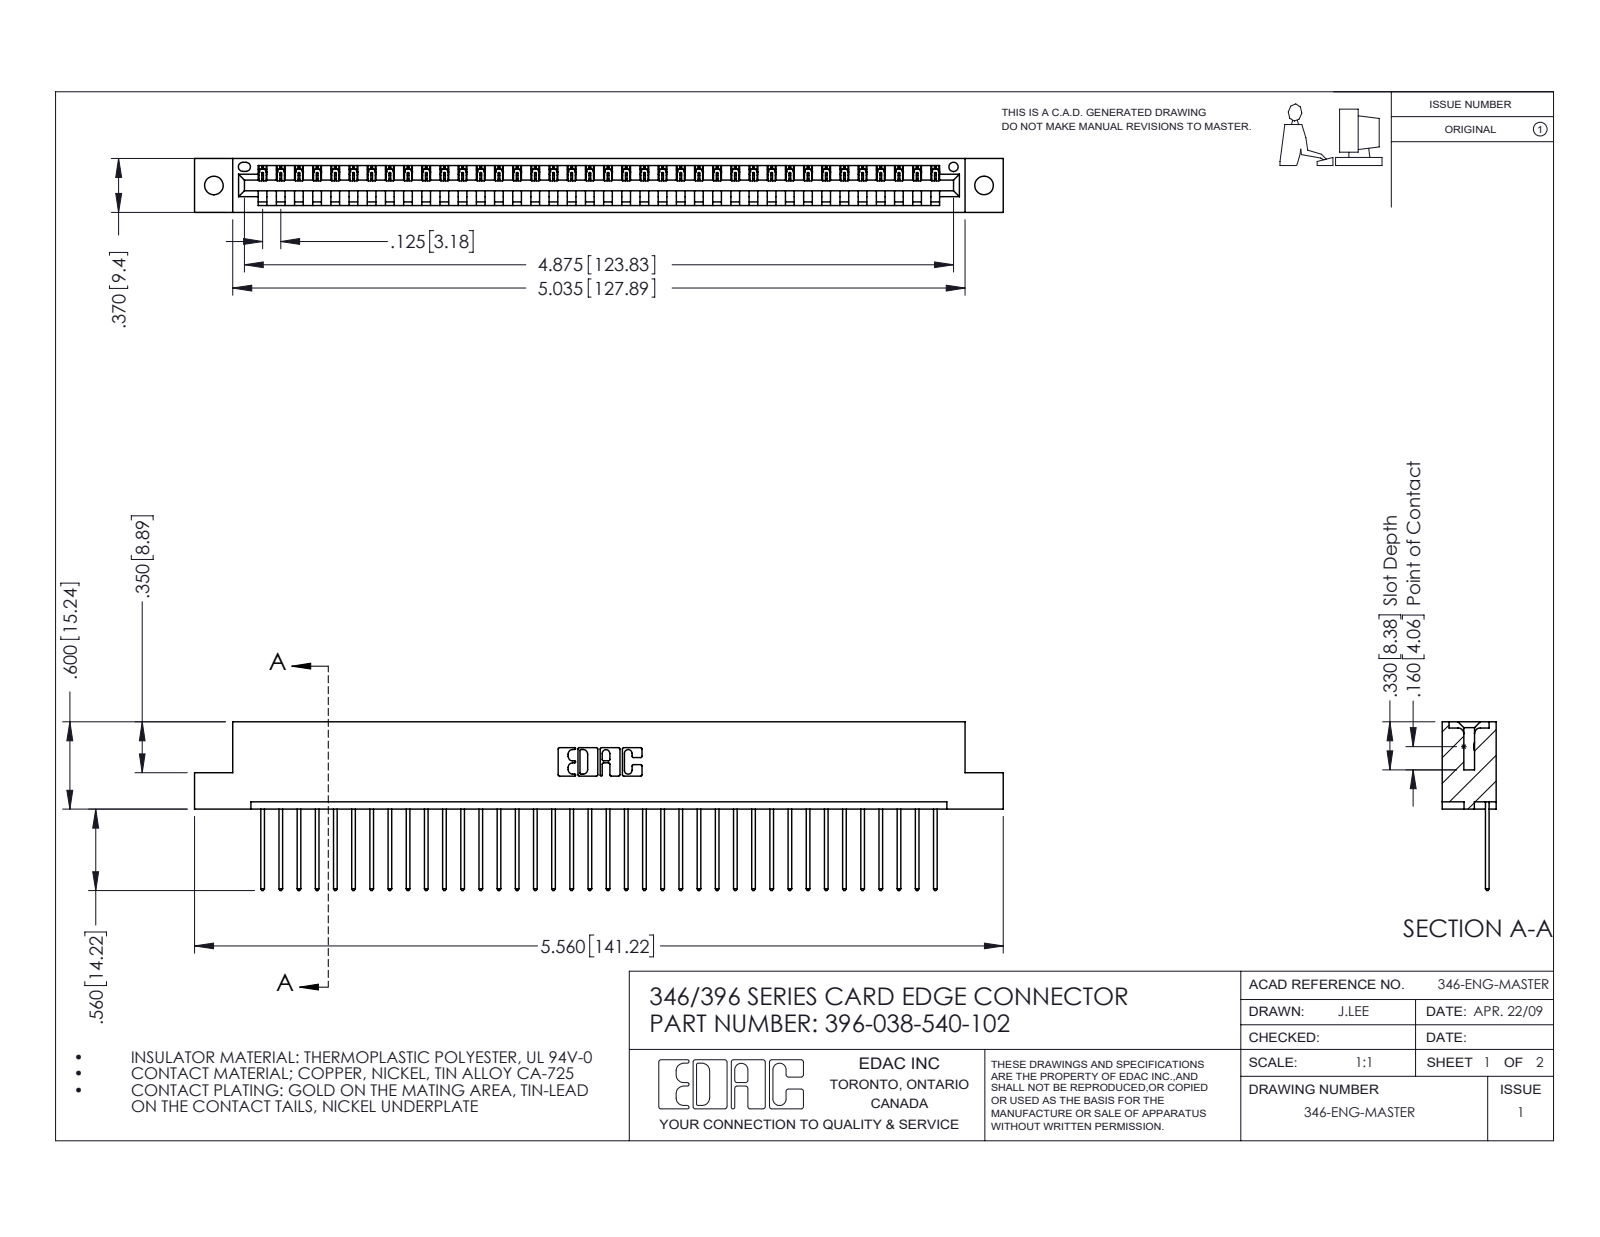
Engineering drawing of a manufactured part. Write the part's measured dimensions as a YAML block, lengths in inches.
part_name: "396-038-540-102; 345-292-001_345-293-140; 346 Part_Flush Mounting Lugs - 0.128 Dia"
step_written_by: "SolidWorks 2016 (CONFIG_CONTROL_DESIGN)"
units: inches
bodies: {solids: 39, faces: 2326, planar: 1596, cylindrical: 730, other: 0}
overall_size: [5.56, 1.16, 0.37]
volume: 0.824
surface_area: 26.26
round_holes:
  - {diameter: 0.128, count: 2}
  - {diameter: 0.064, count: 1}
partial_cylinders:
  - {radius: 0.006, count: 76}
  - {radius: 0.01, count: 76}
  - {radius: 0.01, count: 22}
  - {radius: 0.007, count: 6}
  - {radius: 0.031, count: 6}
  - {radius: 0.026, count: 3}
  - {radius: 0.031, count: 2}
  - {radius: 0.04, count: 2}
face_to_face_distances: [0.048, 0.322, 0.37, 0.25, 0.072, 0.298, 0.025, 0.148, 0.222, 0.1]
hole_center_spacings: [0.246, 5.086, 5.295]
